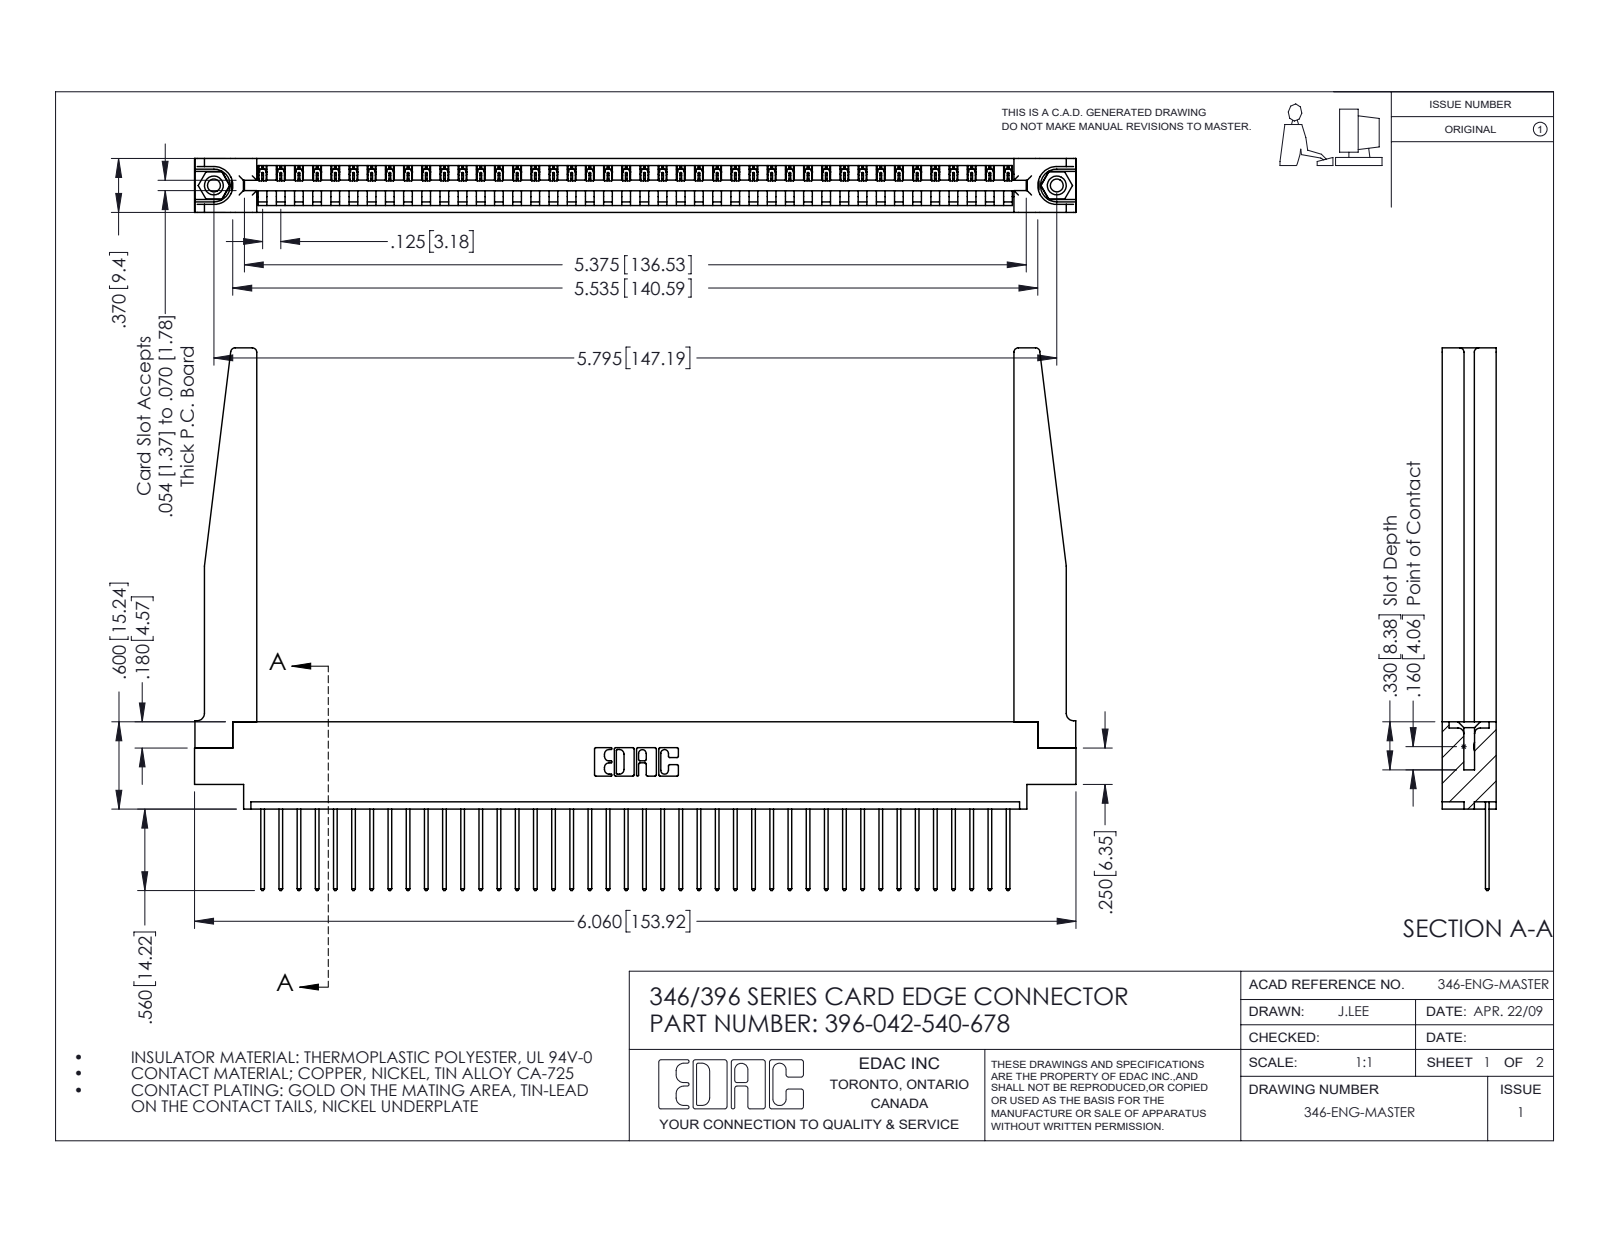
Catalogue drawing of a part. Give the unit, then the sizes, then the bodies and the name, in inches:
Units: inches
Overall size (bounding box): 6.06 × 3.73 × 0.37
Round holes (diameter × count): ⌀0.089 ×2, ⌀0.125 ×2, ⌀0.156 ×2, ⌀0.064 ×1
Round bosses / shafts (diameter × count): ⌀0.155 ×2
Partial cylindrical surfaces — rounded edges, fillets, slot ends (radius × count): R0.006 ×84, R0.01 ×84, R0.01 ×22, R0.03 ×8, R0.007 ×6, R0.031 ×6, R0.026 ×3, R0.031 ×2
Main face-to-face distances: 0.37, 0.048, 0.322, 0.072, 0.148, 0.25, 0.15, 0.298, 0.025, 0.222
Hole centre spacings: 0.246, 5.586, 5.795
Volume: 1.315 in³ · Surface area: 39.38 in²
Bodies: 47 solids, 2796 faces (1902 planar, 842 cylindrical, 52 other)
Part name (STEP PRODUCT): 345-250-001_345-250-001-102; 345-292-001_345-293-140; 346 Part_0.170 Offset - 0.156 Dia-TH; 396-042-540-678 (+1 more)
STEP written by: SolidWorks 2016 (CONFIG_CONTROL_DESIGN)
